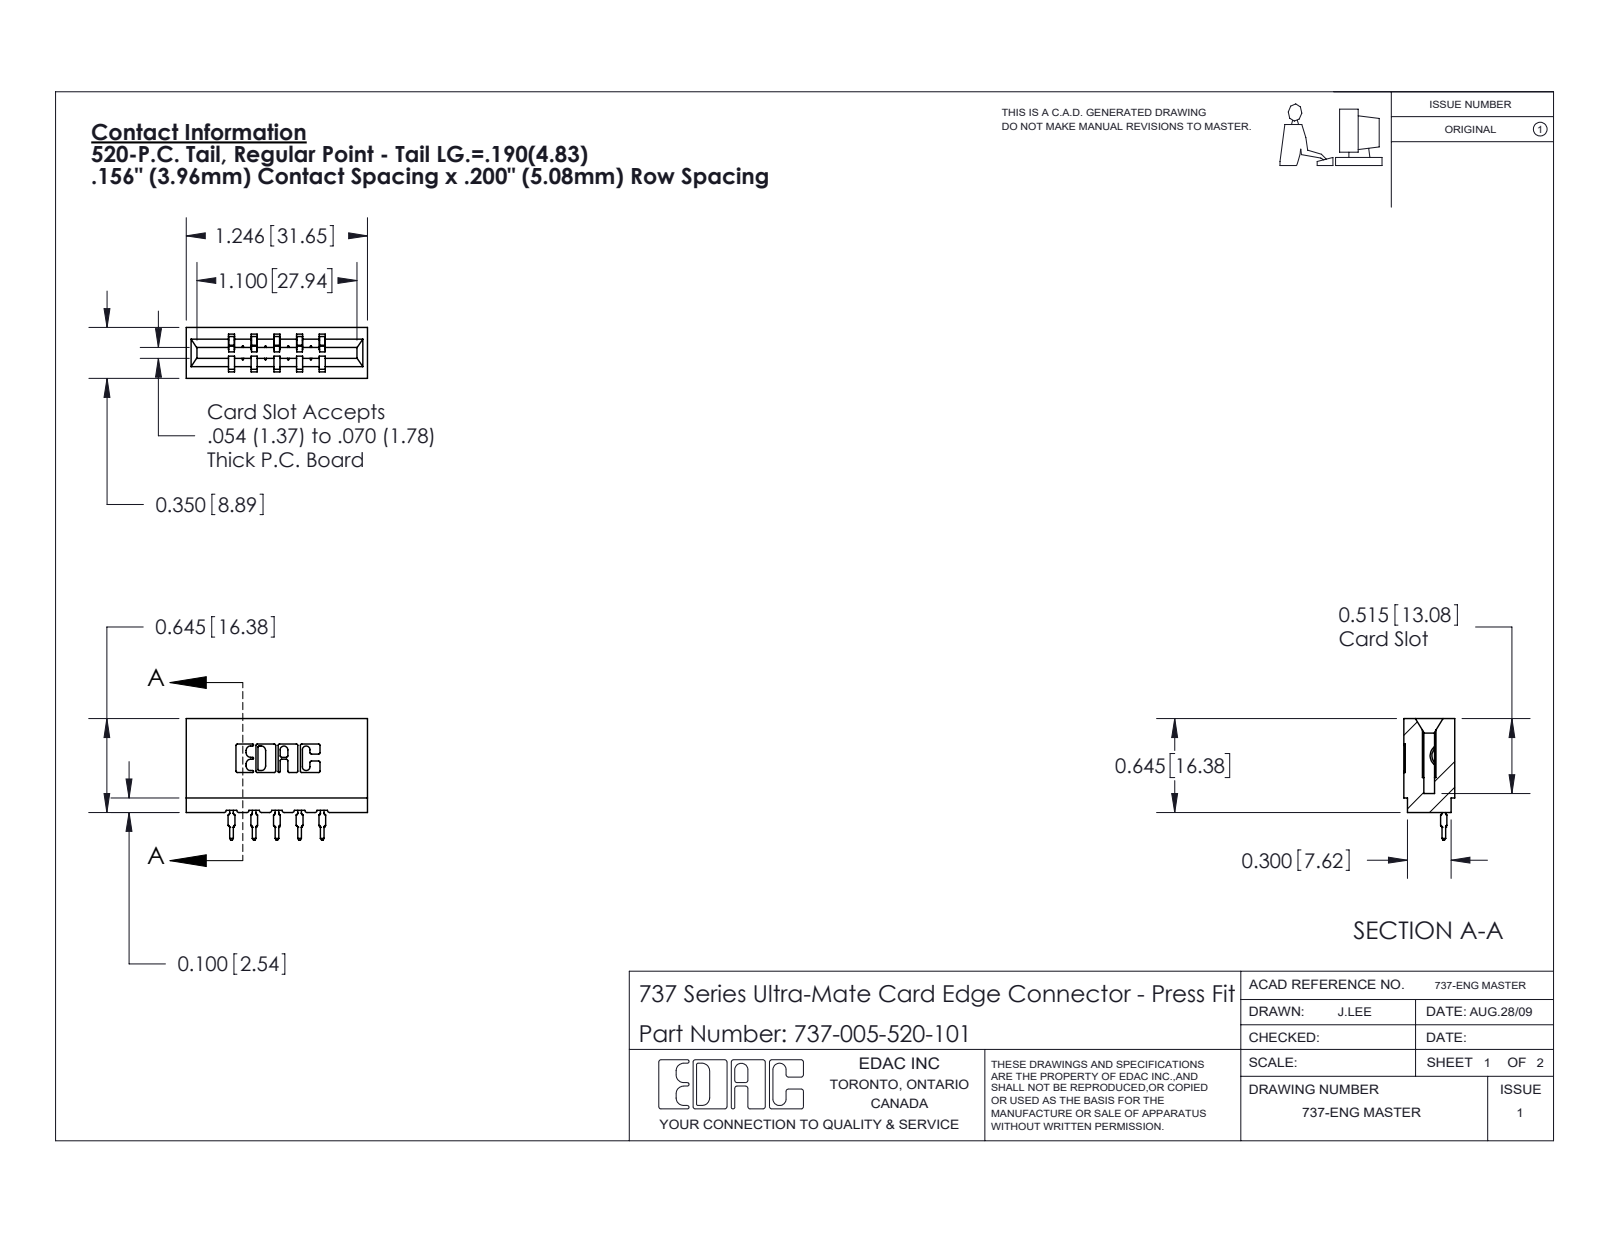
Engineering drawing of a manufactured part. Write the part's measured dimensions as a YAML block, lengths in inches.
part_name: "745-292-001_520; 737-005-520-101; 737 Part_Insulator Option - 01"
step_written_by: "SolidWorks 2020 (CONFIG_CONTROL_DESIGN)"
units: inches
bodies: {solids: 6, faces: 659, planar: 394, cylindrical: 135, other: 130}
overall_size: [1.246, 0.836, 0.35]
volume: 0.202
surface_area: 5.778
partial_cylinders:
  - {radius: 0.01, count: 22}
  - {radius: 0.015, count: 10}
  - {radius: 0.021, count: 10}
  - {radius: 0.007, count: 6}
  - {radius: 0.031, count: 6}
  - {radius: 0.005, count: 4}
  - {radius: 0.011, count: 4}
  - {radius: 0.026, count: 3}
face_to_face_distances: [0.138, 0.212, 0.156, 0.35, 0.312, 0.198, 0.074, 0.354, 0.042, 0.025]
